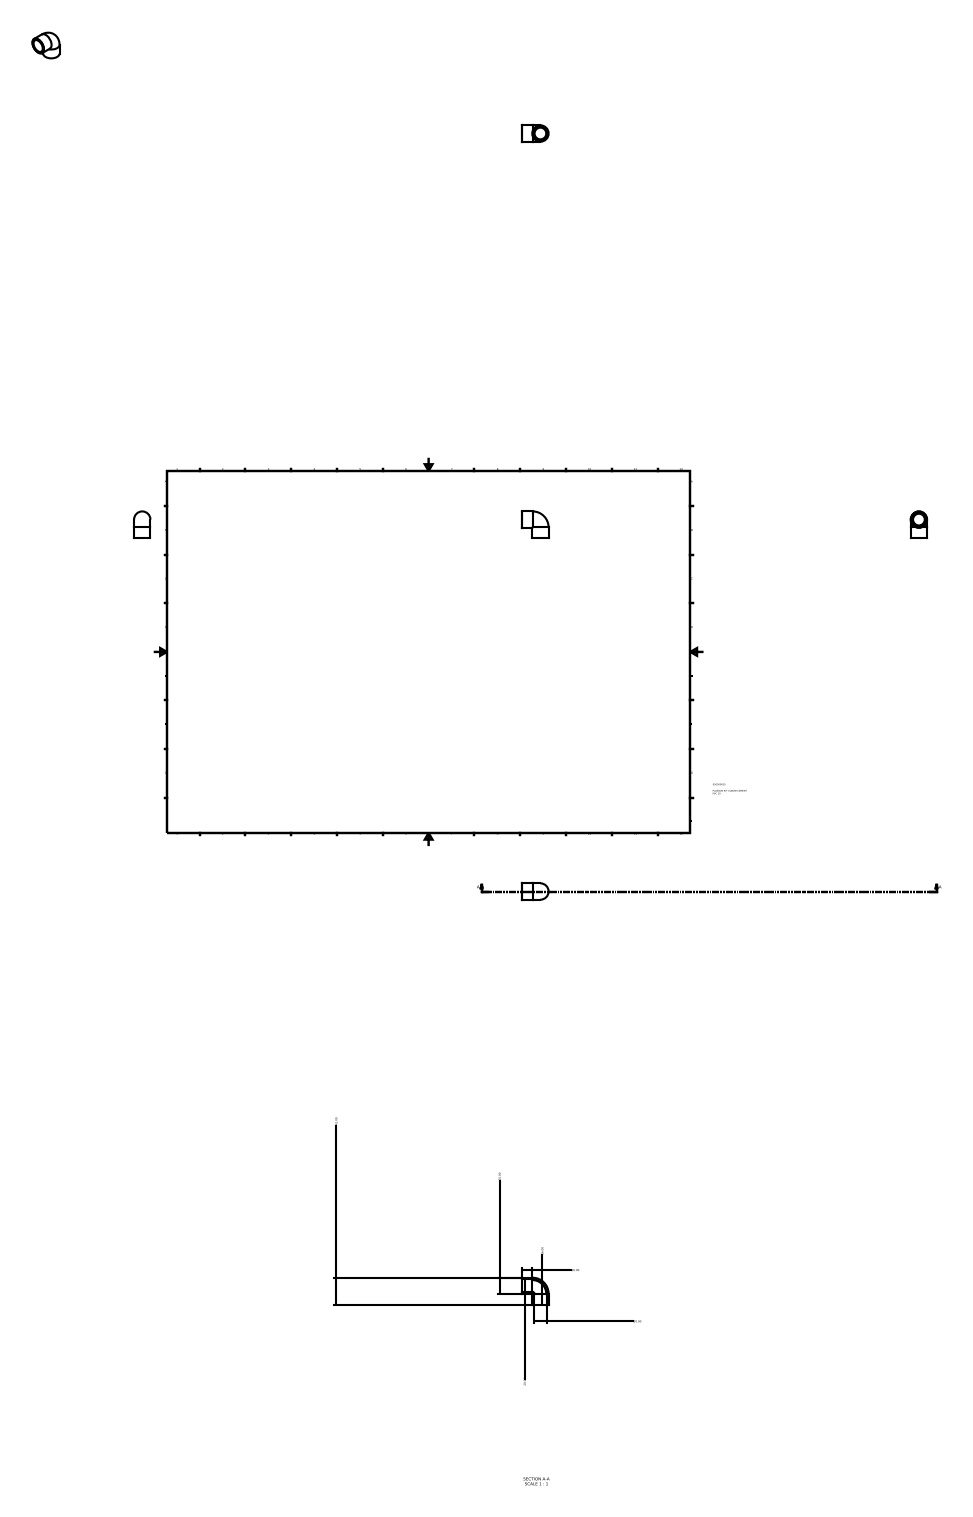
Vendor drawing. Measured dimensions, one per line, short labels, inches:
name: 050500020
written by: Autodesk Inventor 2015 (AUTOMOTIVE_DESIGN)
unit: in
bodies: 1 solid, 11 faces (4 planar, 4 cylindrical, 3 other)
size: 1.614 × 1.614 × 0.984
volume: 0.643 in³; area: 11.87 in²
holes: 2× ⌀0.787
bosses: 2× ⌀0.984
face distances: 0.63
